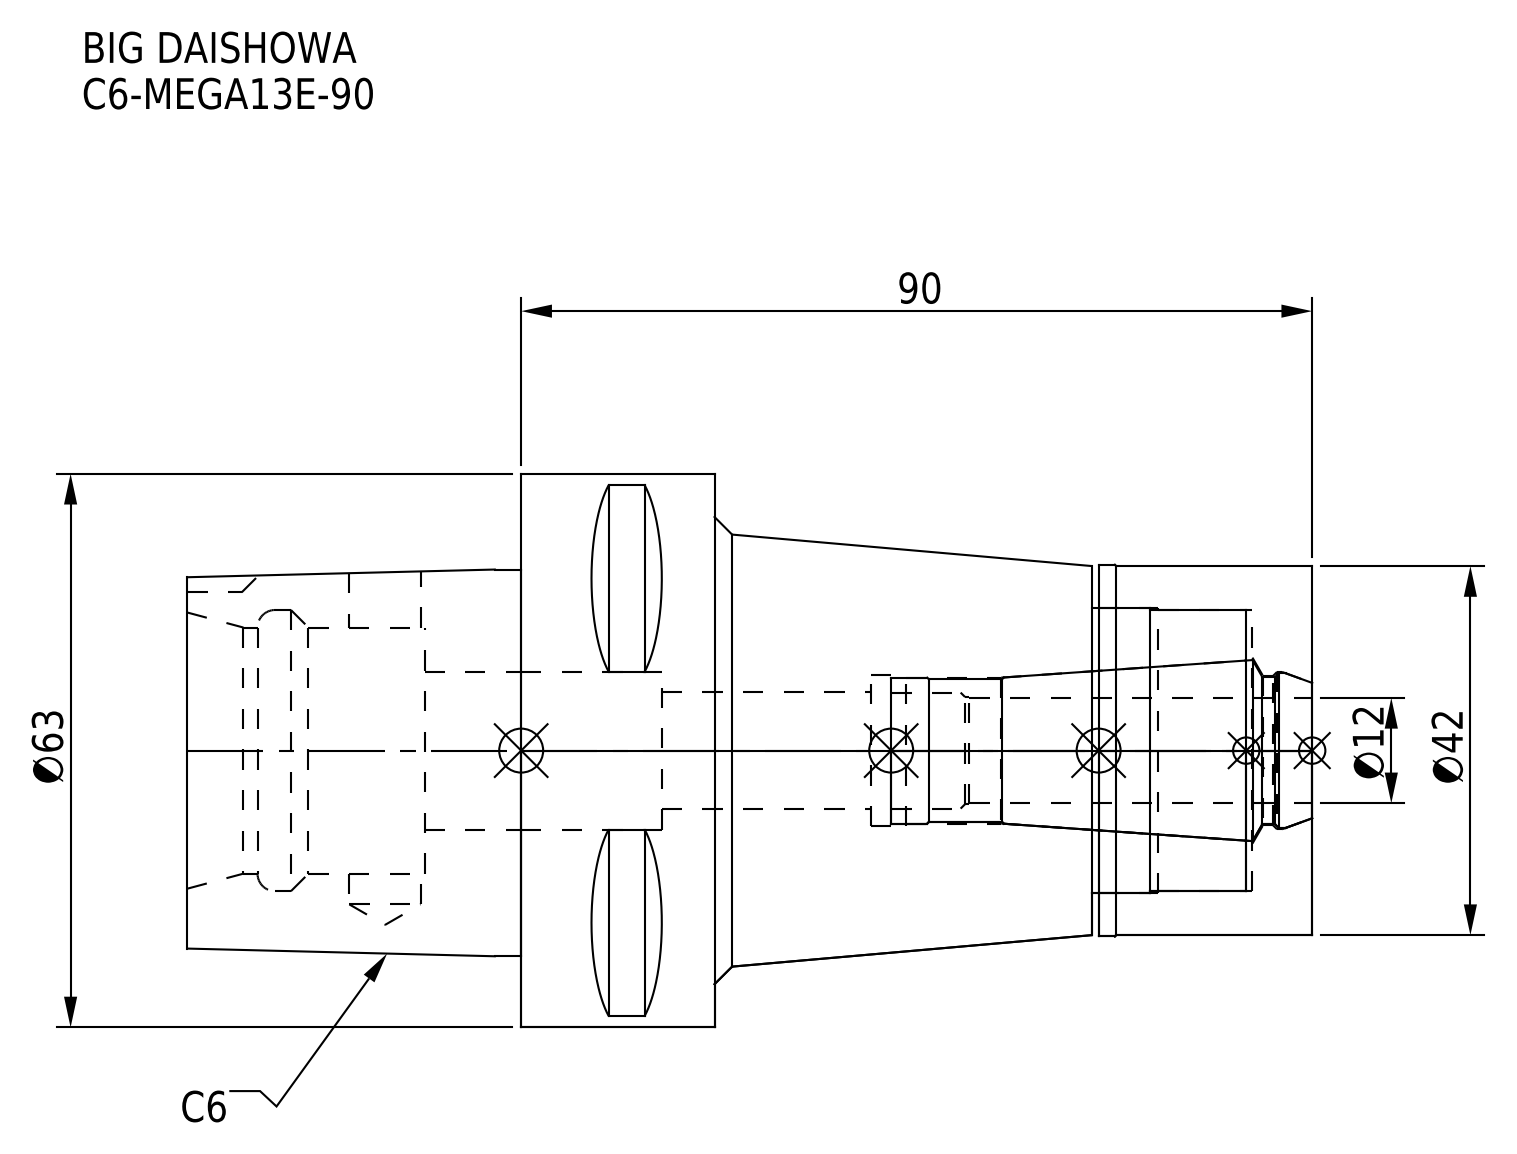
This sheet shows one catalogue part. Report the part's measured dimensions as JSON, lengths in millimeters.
{"part_name": "C6-MEGA13E-90-120-FreeParts; C6-MEGA13E-90-120.stp; C6-MEGA13E-90; DXF_TEMP_ASSY_ASM_4_ASM.stp (+3 more)", "step_written_by": "SolidWorks 2019 (CONFIG_CONTROL_DESIGN)", "units": "millimeters", "bodies": {"solids": 2, "faces": 97, "planar": 36, "cylindrical": 37, "other": 24}, "overall_size": [128, 63, 63], "volume_mm3": 185600, "surface_area_mm2": 38167, "round_holes": [[8.1, 1], [13.3, 1], [16.6, 1], [17, 1], [17.2, 1], [17.9, 1], [18, 1], [28, 1], [32, 1], [32.5, 1]], "round_bosses_or_shafts": [[63, 1], [42.3, 1], [42, 1]], "partial_cylinders_radius": [[5, 1]], "face_to_face_distances": [90, 68, 22, 25.1, 24.3, 43.7, 65.7, 0.8, 42.9, 64.9]}
